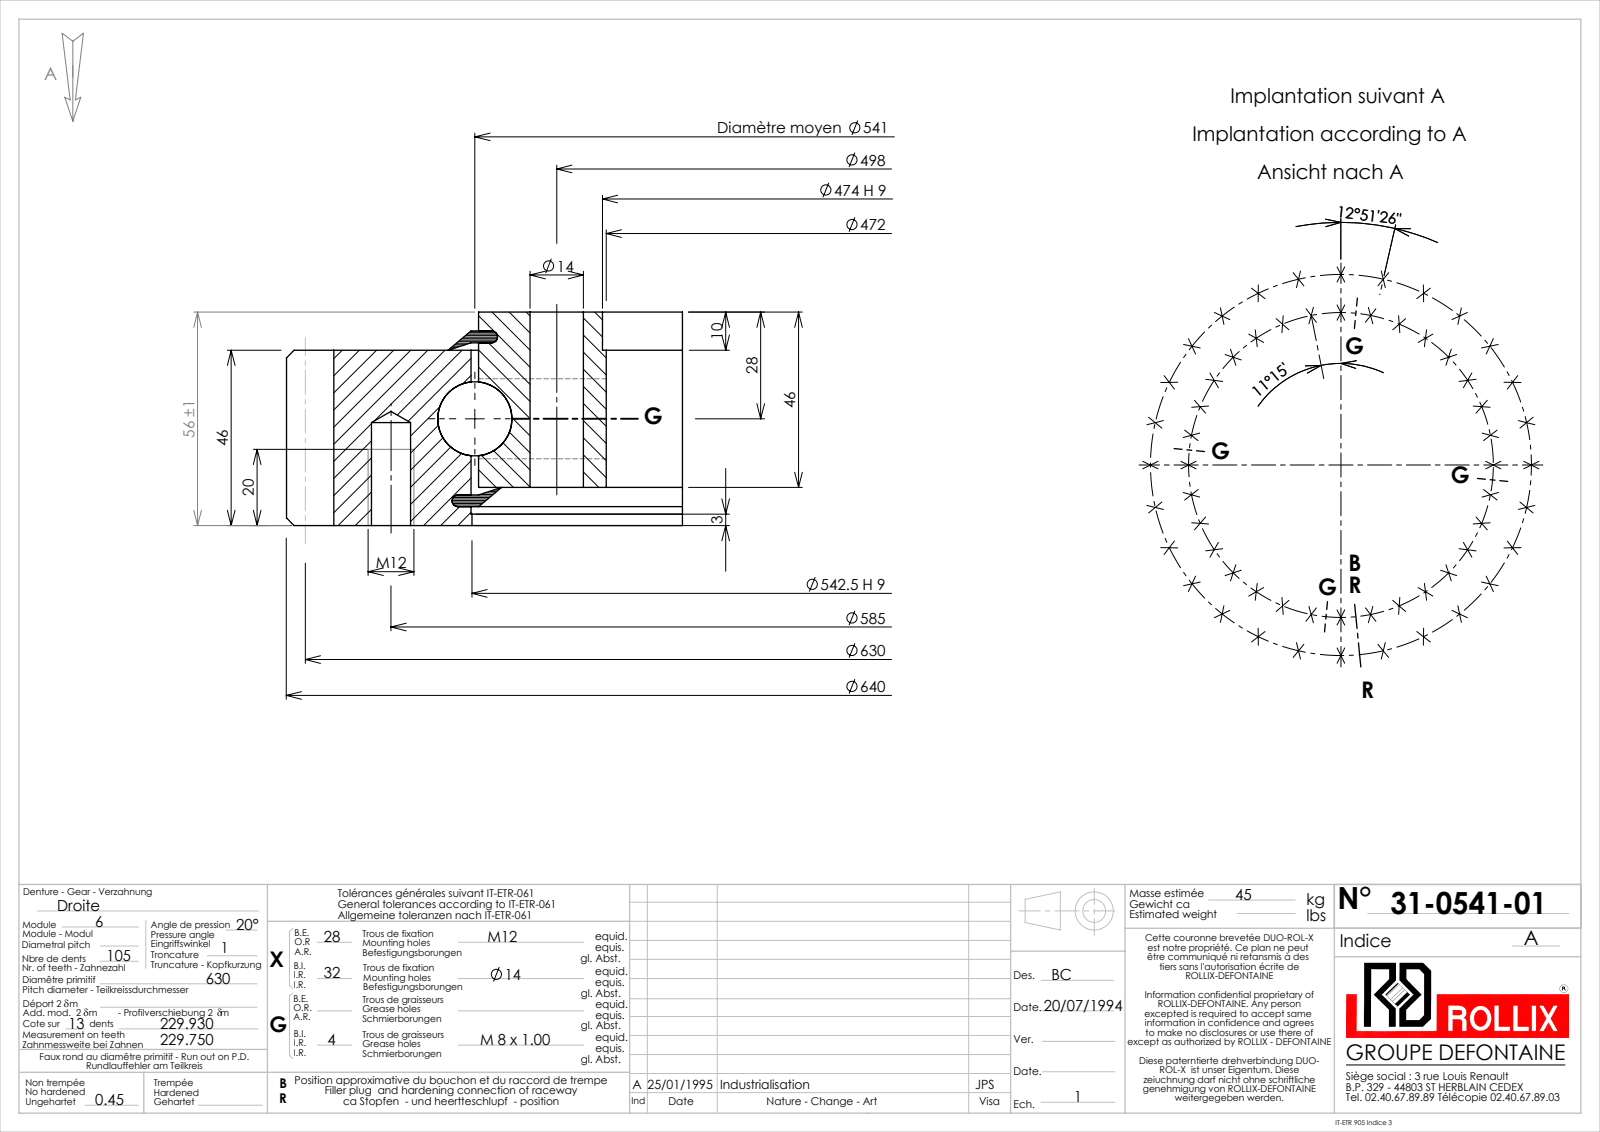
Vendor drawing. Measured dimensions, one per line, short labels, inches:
name: 31-0541-01
written by: SolidWorks 2016 (CONFIG_CONTROL_DESIGN)
unit: in
bodies: 9 solids, 964 faces (264 planar, 365 cylindrical, 335 other)
size: 25.196 × 25.194 × 2.205
volume: 328.7 in³; area: 1 413 in²
holes: 32× ⌀0.551, 28× ⌀0.404, 4× ⌀0.276, 1× ⌀18.583, 1× ⌀18.661, 1× ⌀21.358, 1× ⌀21.376
bosses: 4× ⌀0.315, 1× ⌀21.222
rounds: 1× R12.106, 1× R12.598
face distances: 1.811, 0.394, 1.417, 2.205, 0.077, 0.199, 1.693, 0.317, 1.888, 1.494
hole spacings: 11.516, 14.36, 2.579, 20.751, 9.993, 12.254, 16.286, 5.125
